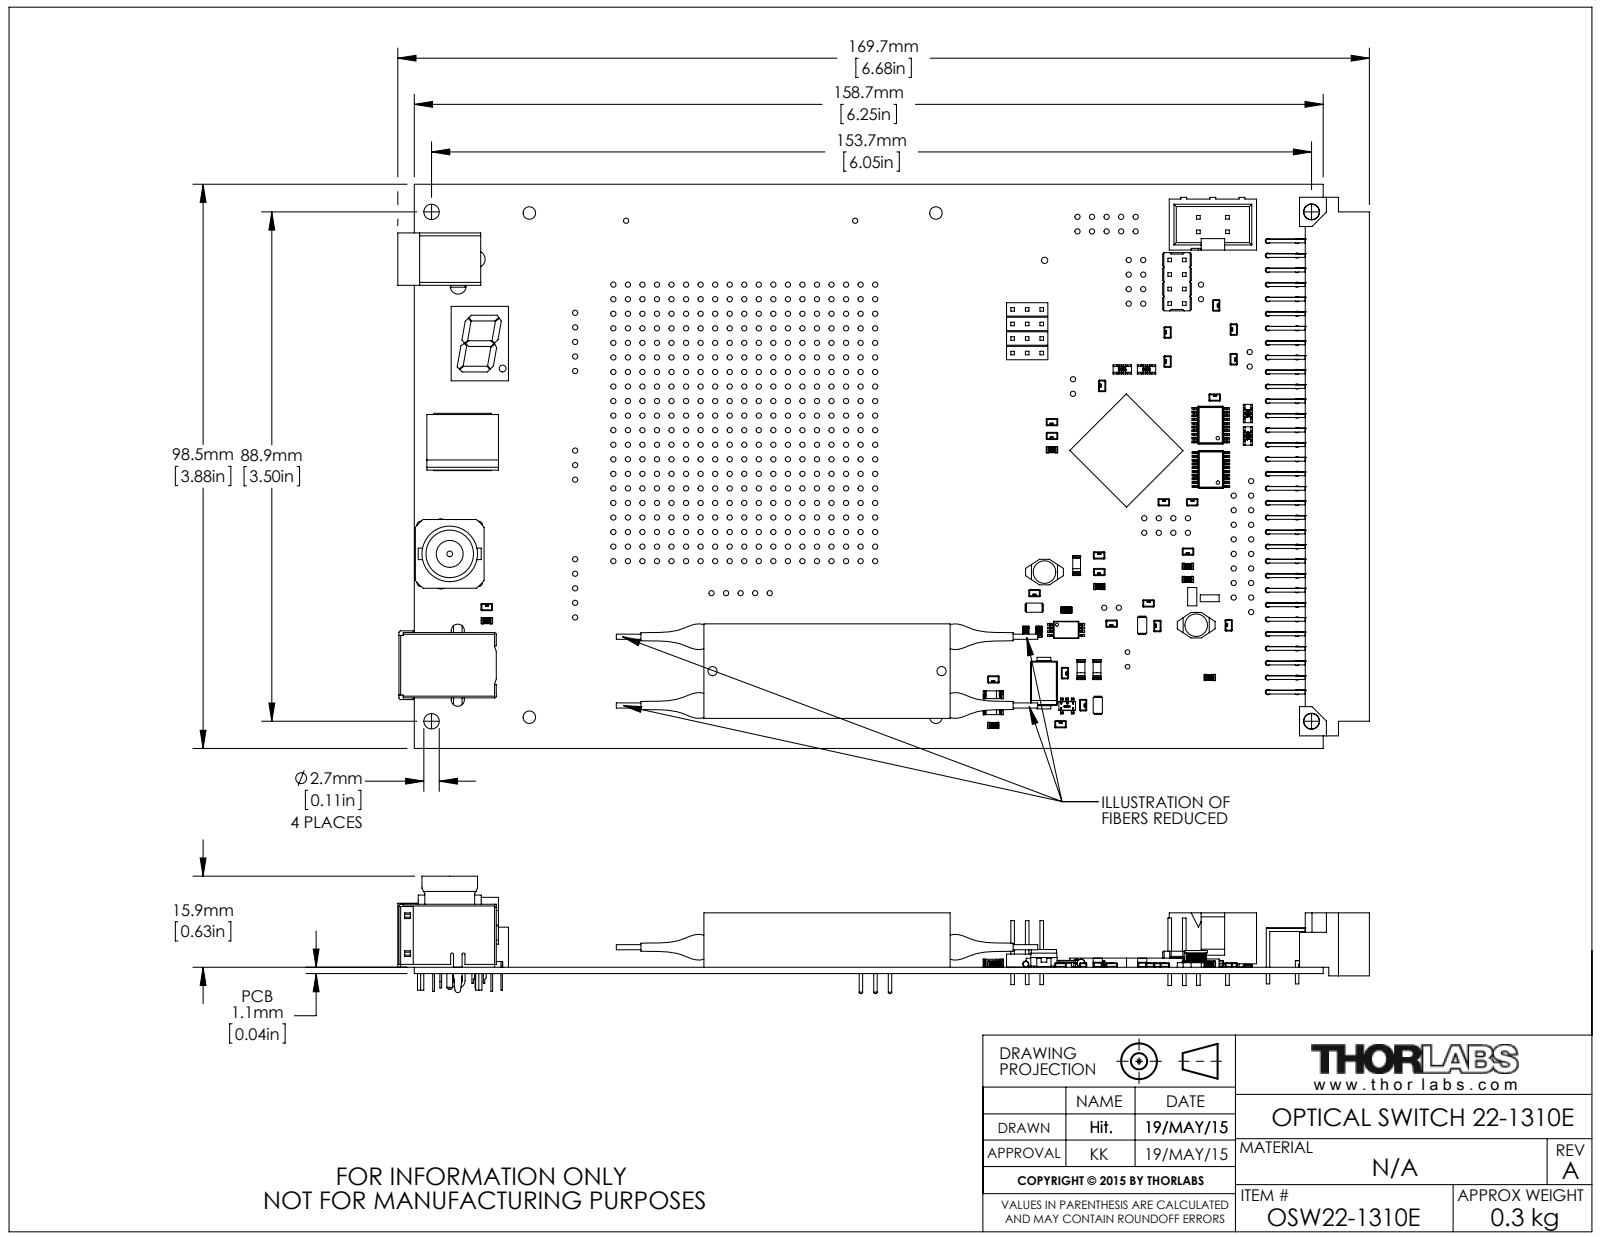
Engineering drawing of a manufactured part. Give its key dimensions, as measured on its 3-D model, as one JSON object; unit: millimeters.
{"part_name": "D4-2141; IC6-2141; User_Library-Melf_0102_Anschl_X_FCsse_1; User_Library-Array-1206-4Way-Var2-1_K_X_F6rper_1 (+8 more)", "step_written_by": "SolidWorks 2014 (AUTOMOTIVE_DESIGN)", "units": "millimeters", "bodies": {"solids": 299, "faces": 8780, "planar": 4332, "cylindrical": 2339, "other": 2109}, "overall_size": [169.66, 98.48, 20.5], "volume_mm3": 37283, "surface_area_mm2": 53901, "round_holes": [[0.91, 542], [0.76, 10], [1, 7], [1.02, 7], [1.32, 5], [1.4, 4], [2.18, 4], [2.69, 4], [1.5, 3], [0.6, 2], [0.81, 2], [1.6, 2]], "round_bosses_or_shafts": [[1, 16], [1.1, 10], [1.4, 5], [1.35, 5], [0.6, 3], [3.94, 2], [2, 2], [0.9, 2]], "partial_cylinders_radius": [[0.15, 330], [0.13, 24], [0.3, 15], [0.2, 10], [0.29, 6], [0.13, 4], [0.25, 2], [0.45, 2]], "face_to_face_distances": [1.1, 10.6, 9.5, 9.85, 1.15, 11, 1.5, 0.6, 0.4, 4.8], "hole_center_spacings": [2.54, 5.08, 5.68, 3.59, 7.62, 15.4, 15.9, 16.1]}
